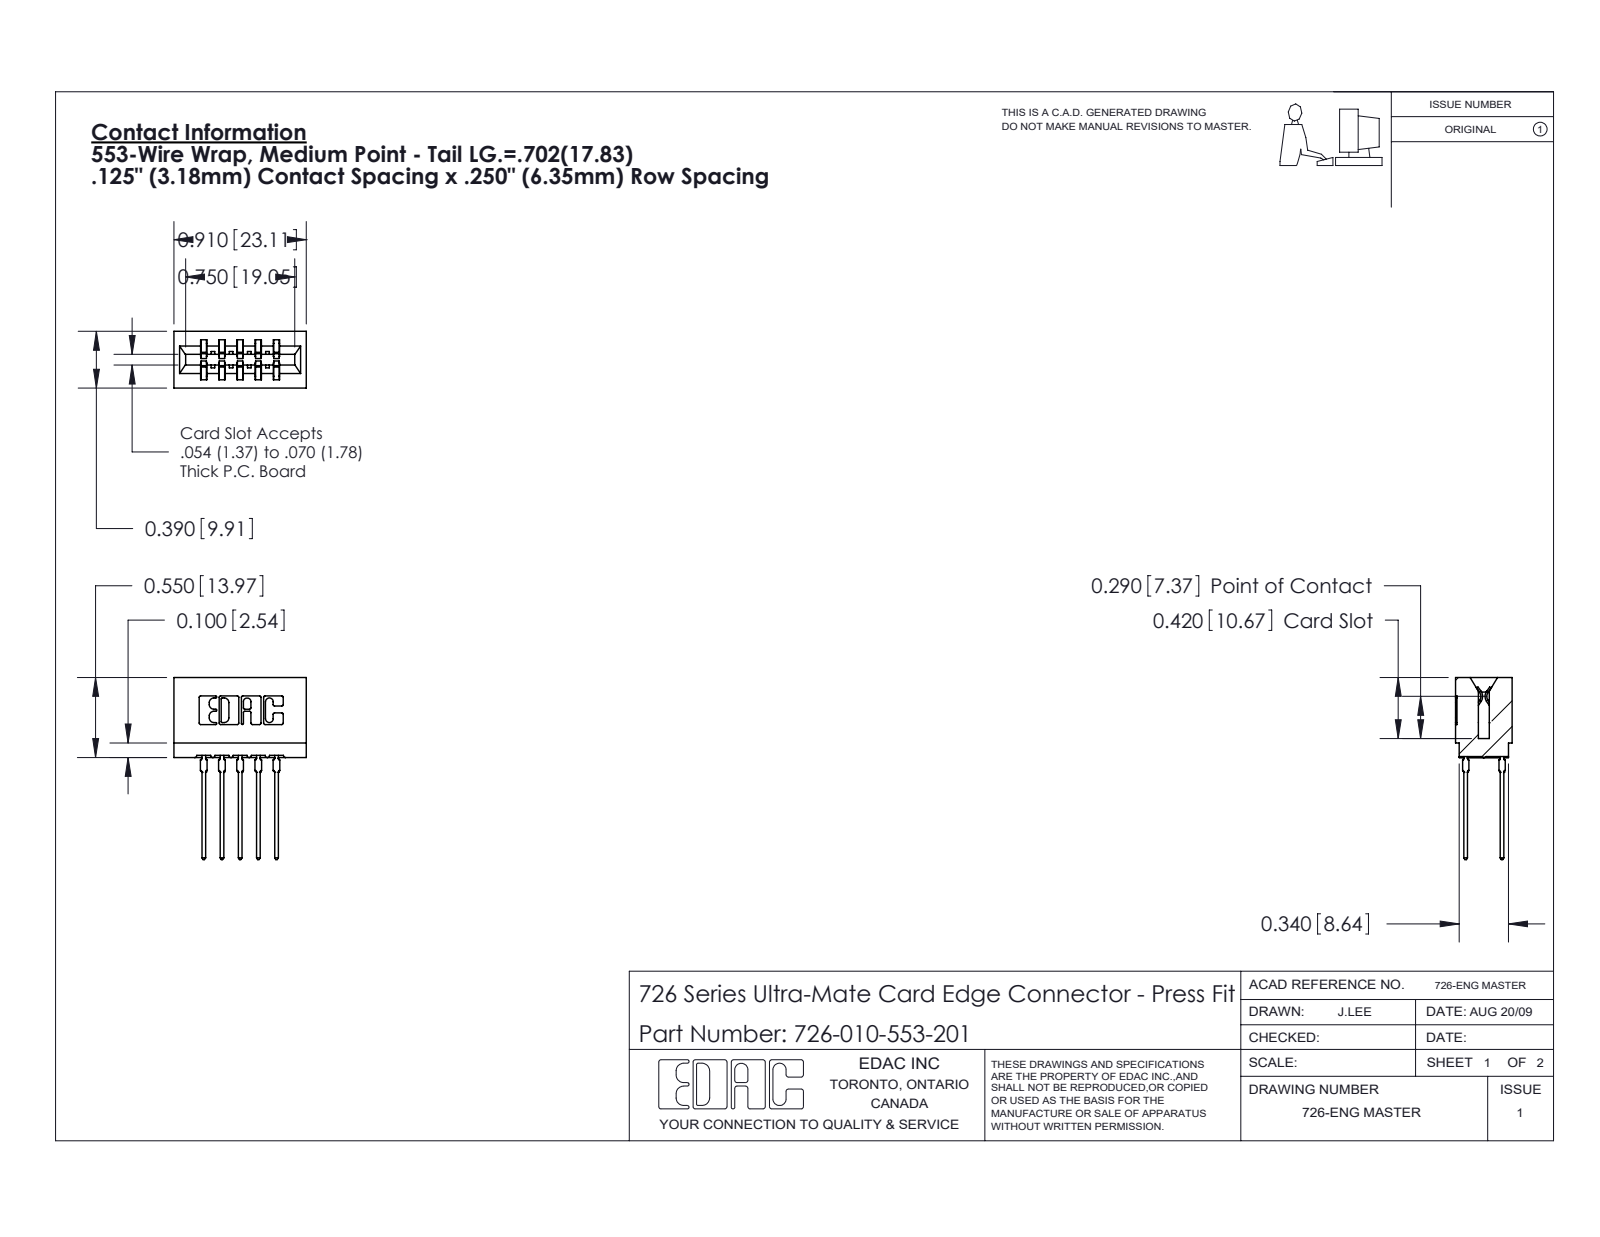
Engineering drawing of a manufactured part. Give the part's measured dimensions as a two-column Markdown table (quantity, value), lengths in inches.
| quantity | value |
| --- | --- |
| part name | 746-292-001_553; 726-010-553-201; 726 Part_.515 Slot Depth - 01 |
| STEP written by | SolidWorks 2020 (CONFIG_CONTROL_DESIGN) |
| units | inches |
| bodies | 11 solids, 992 faces (515 planar, 217 cylindrical, 260 other) |
| overall size | 1.251 × 0.91 × 0.39 |
| volume | 0.144 in³ |
| surface area | 5.412 in² |
| partial cylindrical surfaces (radius × count) | 0.01 × 22, 0.021 × 20, 0.005 × 8, 0.011 × 8, 0.007 × 6, 0.015 × 6, 0.031 × 6, 0.026 × 3 |
| main face-to-face distances | 0.25, 0.057, 0.333, 0.042, 0.125, 0.125, 0.025, 0.083, 0.307, 0.39 |
